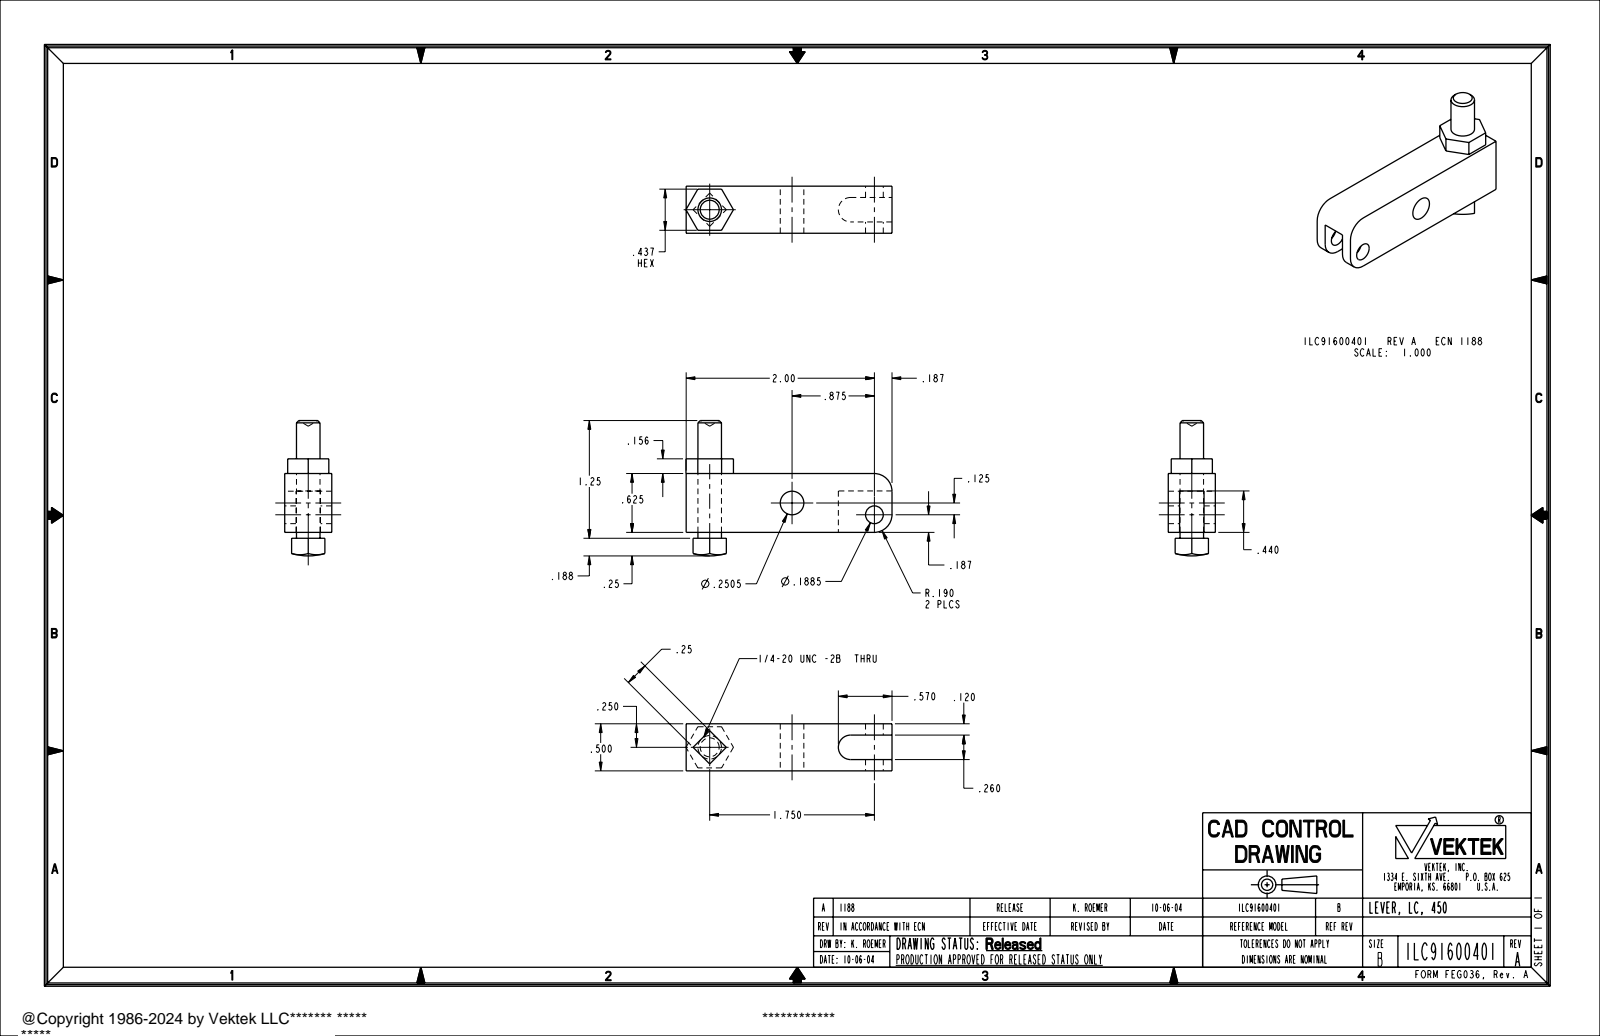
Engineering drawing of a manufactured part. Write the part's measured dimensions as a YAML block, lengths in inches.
part_name: "91600401"
step_written_by: "PRO/ENGINEER BY PARAMETRIC TECHNOLOGY CORPORATION, 2004290 (CONFIG_CONTROL_DESIGN)"
units: inches
bodies: {solids: 1, faces: 48, planar: 26, cylindrical: 16, other: 6}
overall_size: [2.189, 1.437, 0.5]
volume: 0.644
surface_area: 7.504
round_holes:
  - {diameter: 0.189, count: 1}
  - {diameter: 0.25, count: 1}
round_bosses_or_shafts:
  - {diameter: 0.25, count: 1}
partial_cylinders:
  - {radius: 0.19, count: 2}
  - {radius: 0.13, count: 1}
face_to_face_distances: [0.5, 0.625, 0.12, 0.38, 0.26, 0.44, 0.185, 0.437, 0.781, 0.341]
hole_center_spacings: [0.883]
